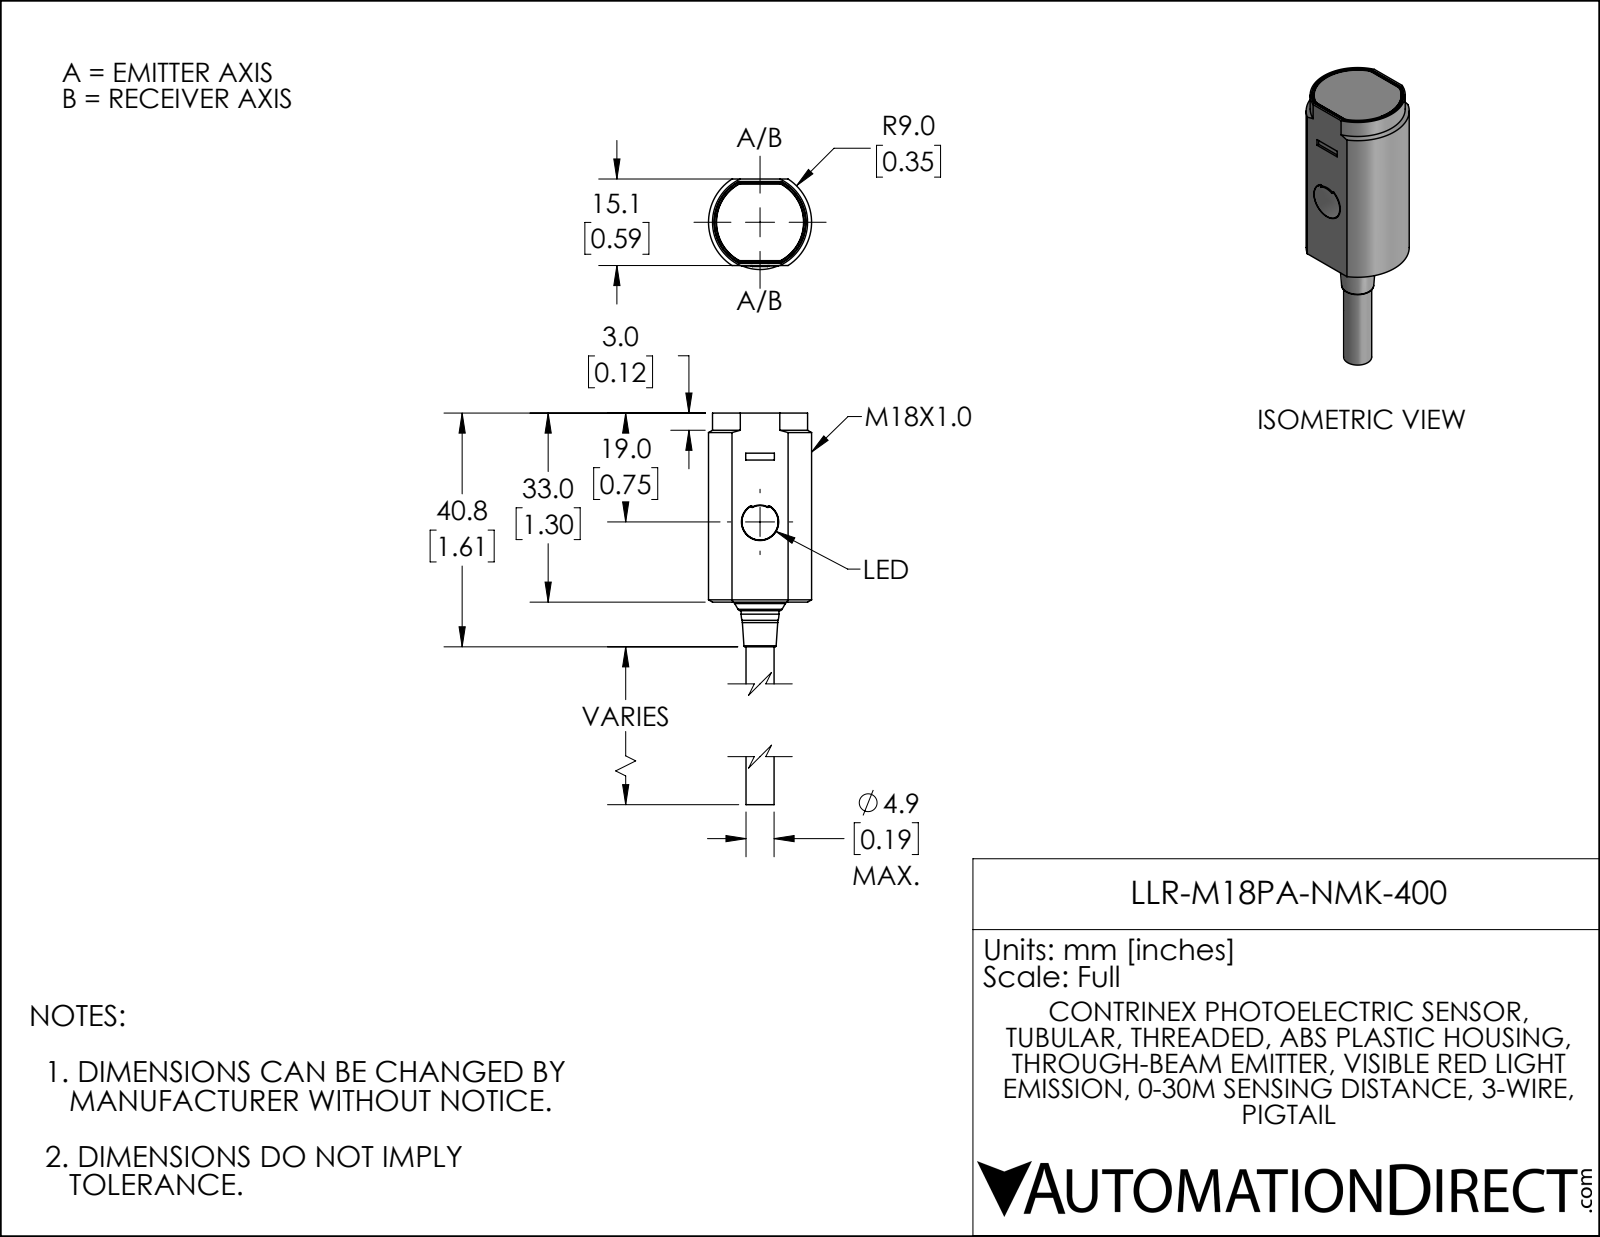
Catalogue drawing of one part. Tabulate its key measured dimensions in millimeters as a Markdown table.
| quantity | value |
| --- | --- |
| part name | LLR-M18PA-NMK-400 |
| STEP written by | SolidWorks 2021 (AUTOMOTIVE_DESIGN) |
| units | millimeters |
| bodies | 1 solid, 93 faces (39 planar, 41 cylindrical, 13 other) |
| overall size | 56 × 18 × 15.8 |
| volume | 8 210 mm³ |
| surface area | 2 729 mm² |
| round holes (diameter × count) | 6.5 × 1 |
| round bosses / shafts (diameter × count) | 6.6 × 1, 4.9 × 1 |
| partial cylindrical surfaces (radius × count) | 0.2 × 8, 0.4 × 8, 0.7 × 8, 2.8 × 1, 2.9 × 1, 7.6 × 1, 7.7 × 1, 8 × 1 |
| main face-to-face distances | 15.1, 32.9, 33, 0.4, 56, 56, 23, 14.7, 0.4, 14.3 |
